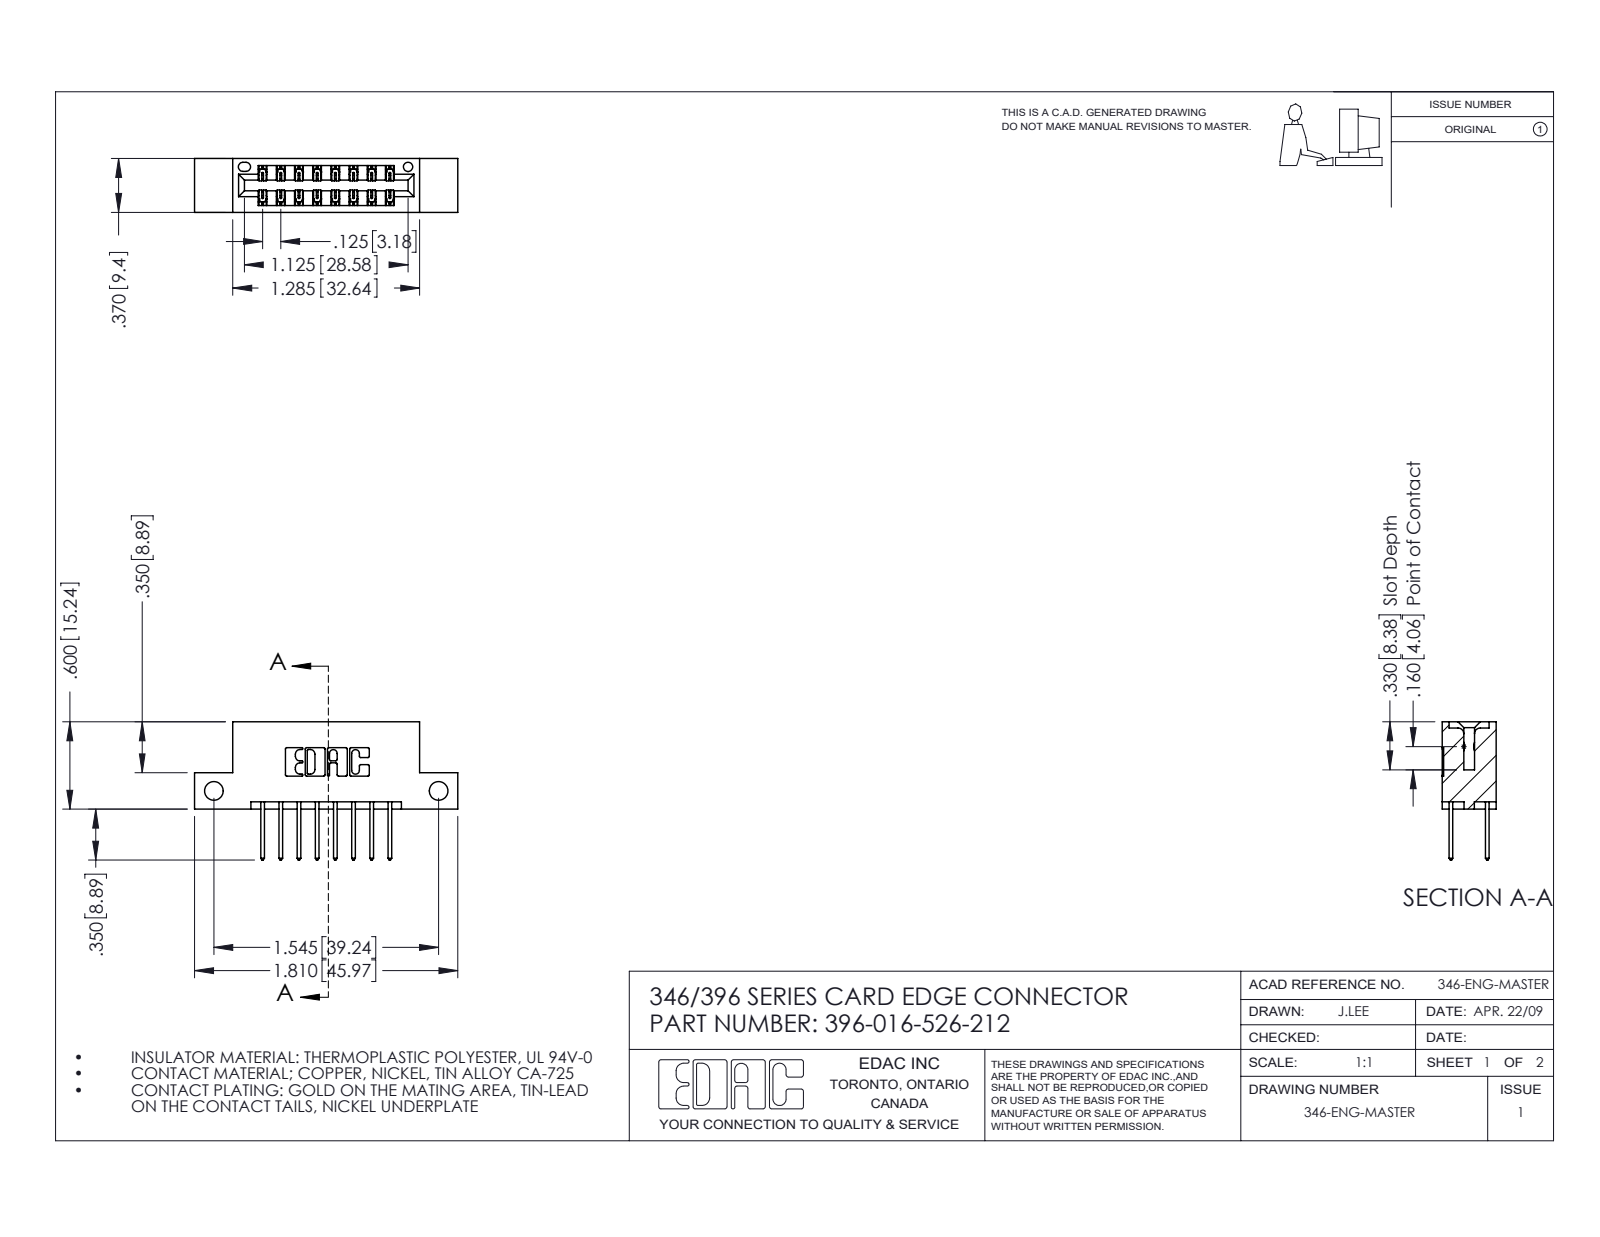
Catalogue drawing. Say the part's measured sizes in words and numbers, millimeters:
The part is named "345-292-001_345-293-126; 396-016-526-212; 346 Part_Flush Mounting Lugs - Side Mount". Its 3-D file was written by "SolidWorks 2016 (CONFIG_CONTROL_DESIGN)". It is 17 solids with 954 faces: 636 planar, 318 cylindrical and 0 other. Overall it measures 46 by 24.1 by 9.4 millimeters. Its volume is 4 160 cubic millimeters and its surface area 5 161 square millimeters. Round holes: 2 of diameter 3.3, 1 of diameter 1.6. Partial cylindrical surfaces (rounded edges, fillets, slot ends): 24 of radius 0.2, 22 of radius 0.3, 16 of radius 0.3, 6 of radius 0.2, 6 of radius 0.8, 3 of radius 0.7, 2 of radius 0.4, 2 of radius 0.6. The main face-to-face distances are 6.4, 1.2, 8.2, 9.4, 1.8, 7.6, 0.6, 7, 12.7, 3.8. The hole center spacings are 39.2.
